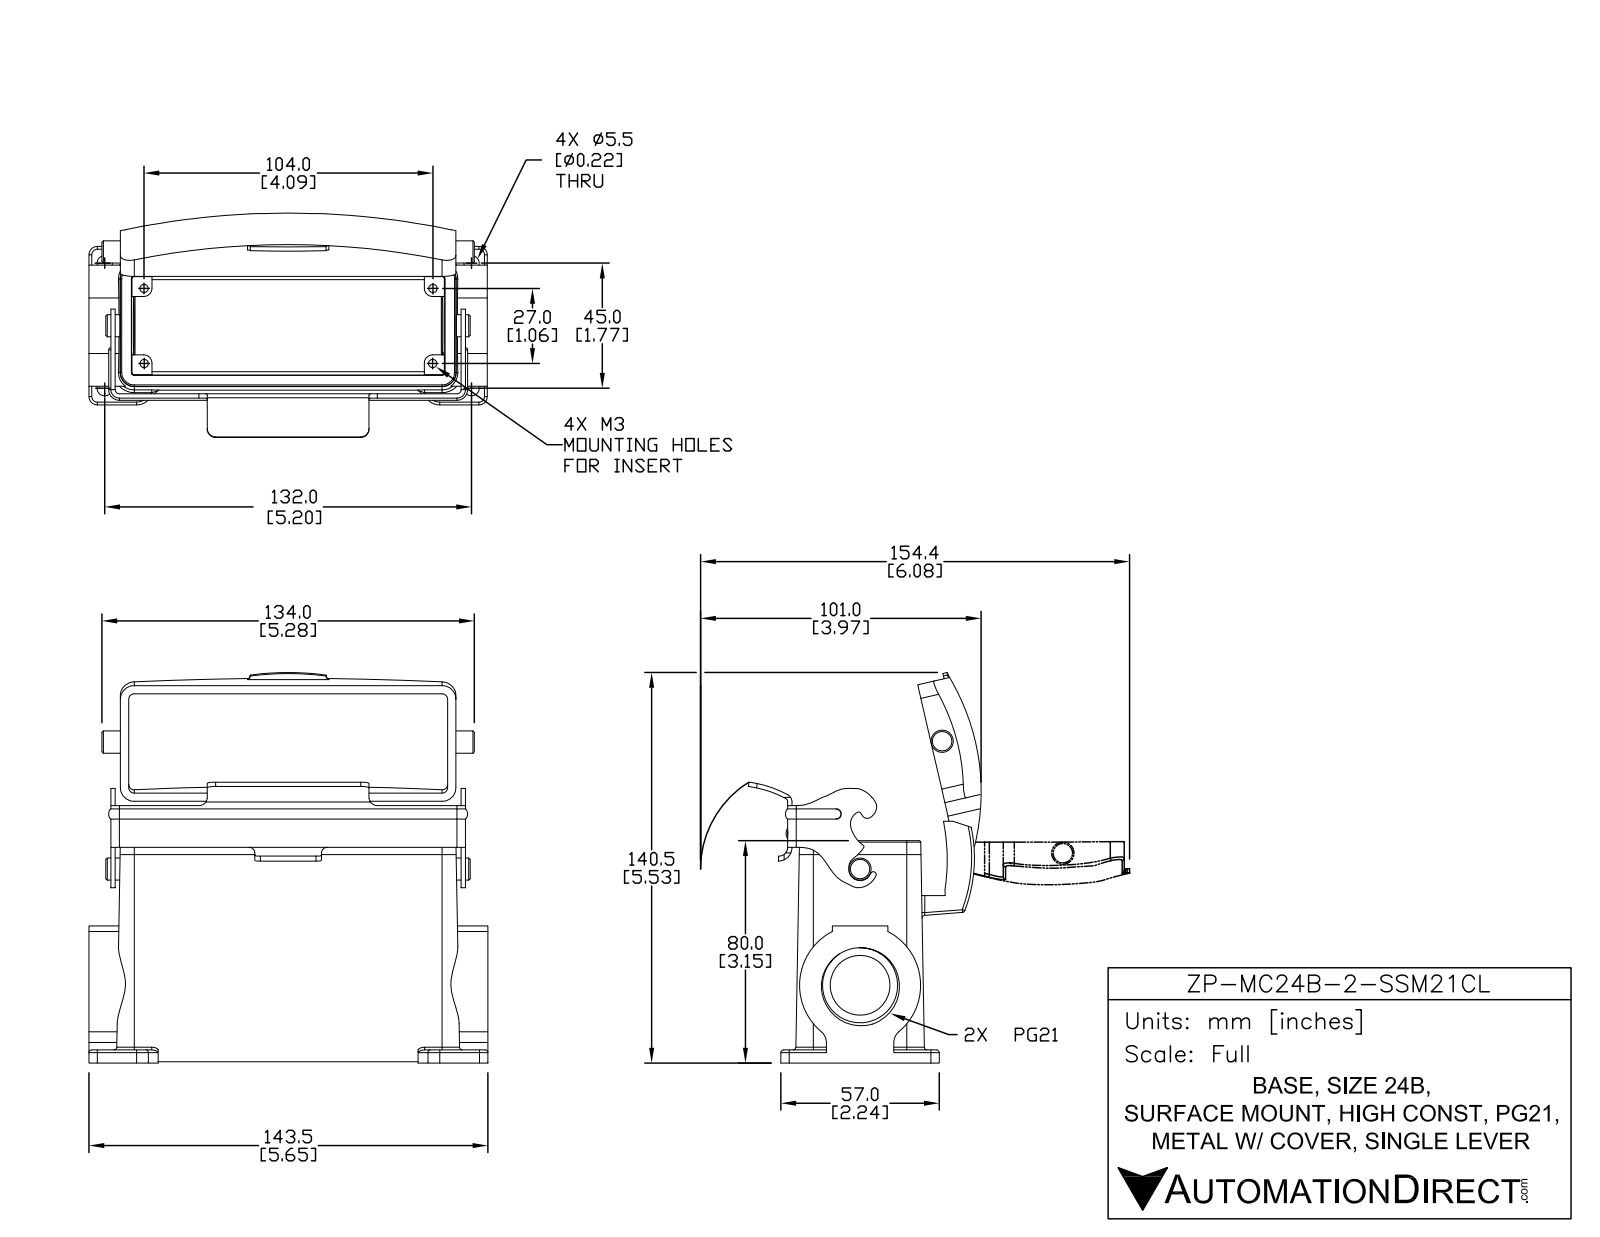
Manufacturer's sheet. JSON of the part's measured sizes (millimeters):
{"part_name": "ZP-MC24B-2-SSM21CL", "step_written_by": "SolidWorks 2014 (AUTOMOTIVE_DESIGN)", "units": "millimeters", "bodies": {"solids": 3, "faces": 404, "planar": 160, "cylindrical": 166, "other": 78}, "overall_size": [143.32, 140.5, 80.75], "volume_mm3": 214307, "surface_area_mm2": 98700, "round_holes": [[3, 4], [5.5, 4], [2, 1], [21.5, 1], [27, 1]], "round_bosses_or_shafts": [[8, 1], [7.95, 1], [6.8, 1]], "partial_cylinders_radius": [[1, 18], [3, 12], [2, 8], [5, 8], [0.5, 4], [6, 4], [1.5, 2], [3.06, 2]], "face_to_face_distances": [39.67, 4, 0.5, 4.5, 116.8, 3, 1.56, 40.48, 7.86, 14.8], "hole_center_spacings": [16.64, 38.63, 118.34, 123.37, 27, 45, 104, 107.45]}
